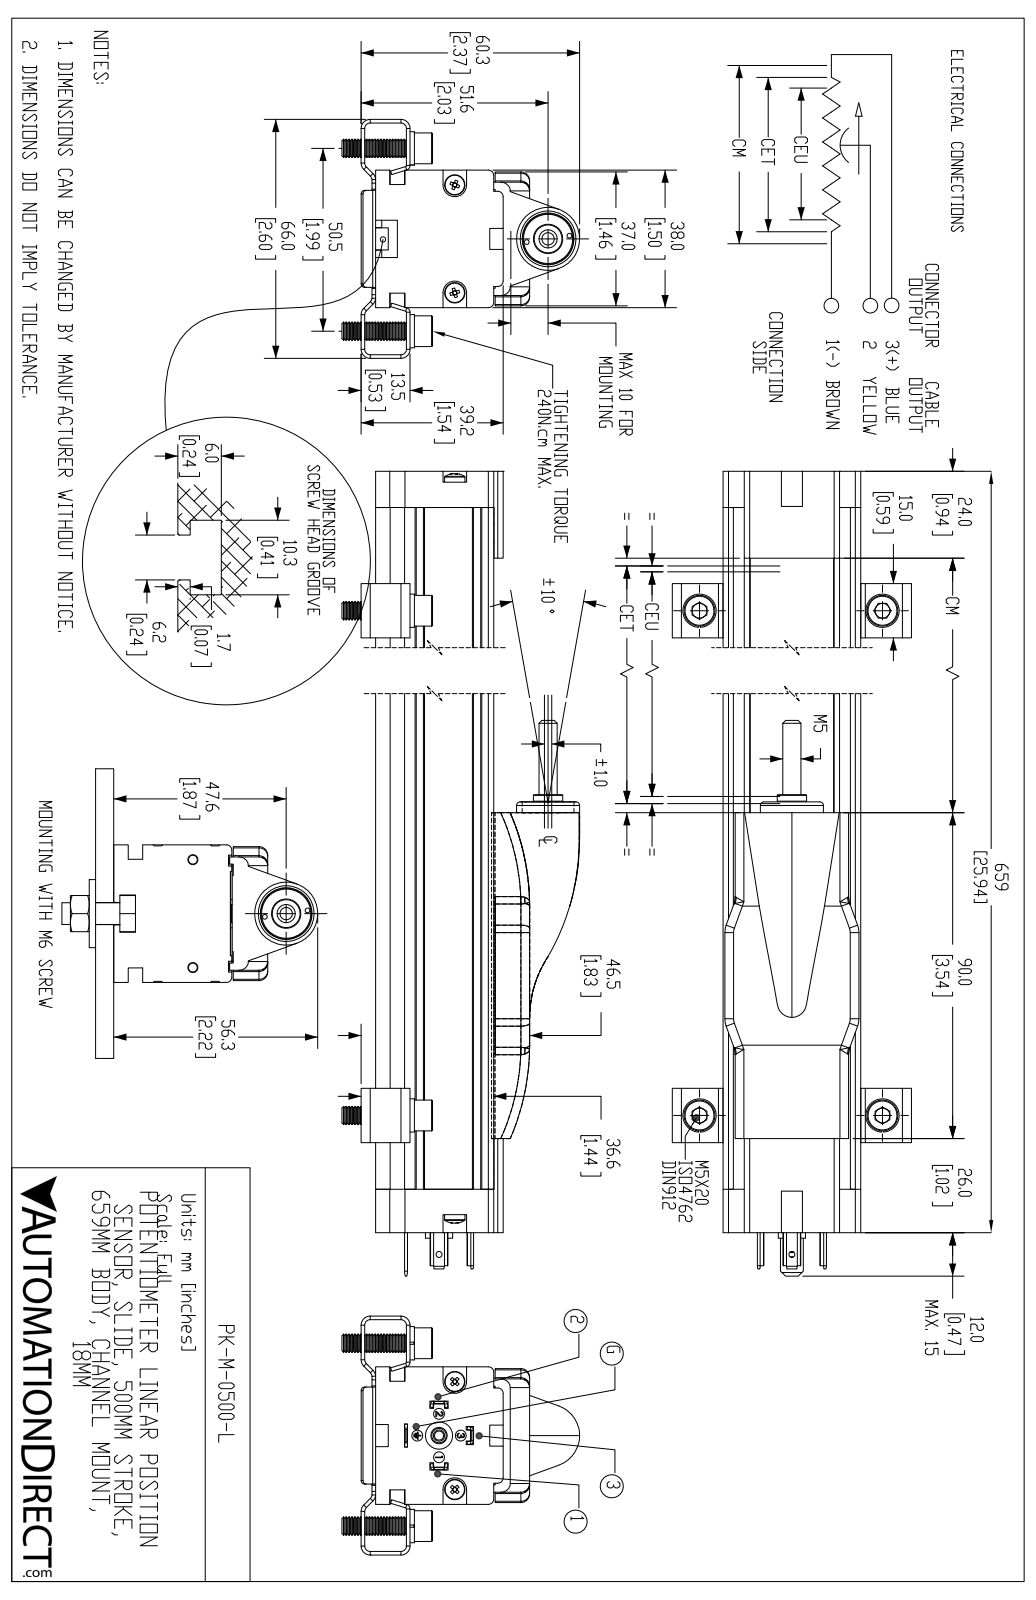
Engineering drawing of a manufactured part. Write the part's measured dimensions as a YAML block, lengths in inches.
part_name: "PK-M-0500-L"
step_written_by: "SolidWorks 2019 (AUTOMOTIVE_DESIGN)"
units: inches
bodies: {solids: 27, faces: 1761, planar: 785, cylindrical: 384, other: 592}
overall_size: [26.417, 2.598, 2.583]
volume: 47.87
surface_area: 300.3
round_holes:
  - {diameter: 0.118, count: 5}
  - {diameter: 0.201, count: 4}
  - {diameter: 0.051, count: 2}
  - {diameter: 0.059, count: 2}
  - {diameter: 0.065, count: 2}
  - {diameter: 0.102, count: 2}
  - {diameter: 0.108, count: 2}
  - {diameter: 0.13, count: 2}
  - {diameter: 0.209, count: 2}
  - {diameter: 0.063, count: 1}
  - {diameter: 0.098, count: 1}
  - {diameter: 0.157, count: 1}
round_bosses_or_shafts:
  - {diameter: 0.197, count: 7}
  - {diameter: 0.362, count: 4}
  - {diameter: 0.335, count: 4}
  - {diameter: 0.22, count: 2}
  - {diameter: 0.118, count: 2}
  - {diameter: 0.098, count: 2}
  - {diameter: 0.685, count: 1}
  - {diameter: 0.551, count: 1}
partial_cylinders:
  - {radius: 0.039, count: 28}
  - {radius: 0.059, count: 12}
  - {radius: 0.098, count: 8}
  - {radius: 0.104, count: 8}
  - {radius: 0.236, count: 8}
  - {radius: 0.033, count: 6}
  - {radius: 0.094, count: 6}
  - {radius: 0.024, count: 4}
face_to_face_distances: [1.268, 0.157, 1.272, 1.496, 0.079, 0.02, 0.039, 1.035, 0.016, 0.315]
hole_center_spacings: [0.236, 0.334, 0.234, 0.39, 0.472, 0.484, 0.539, 0.59]
